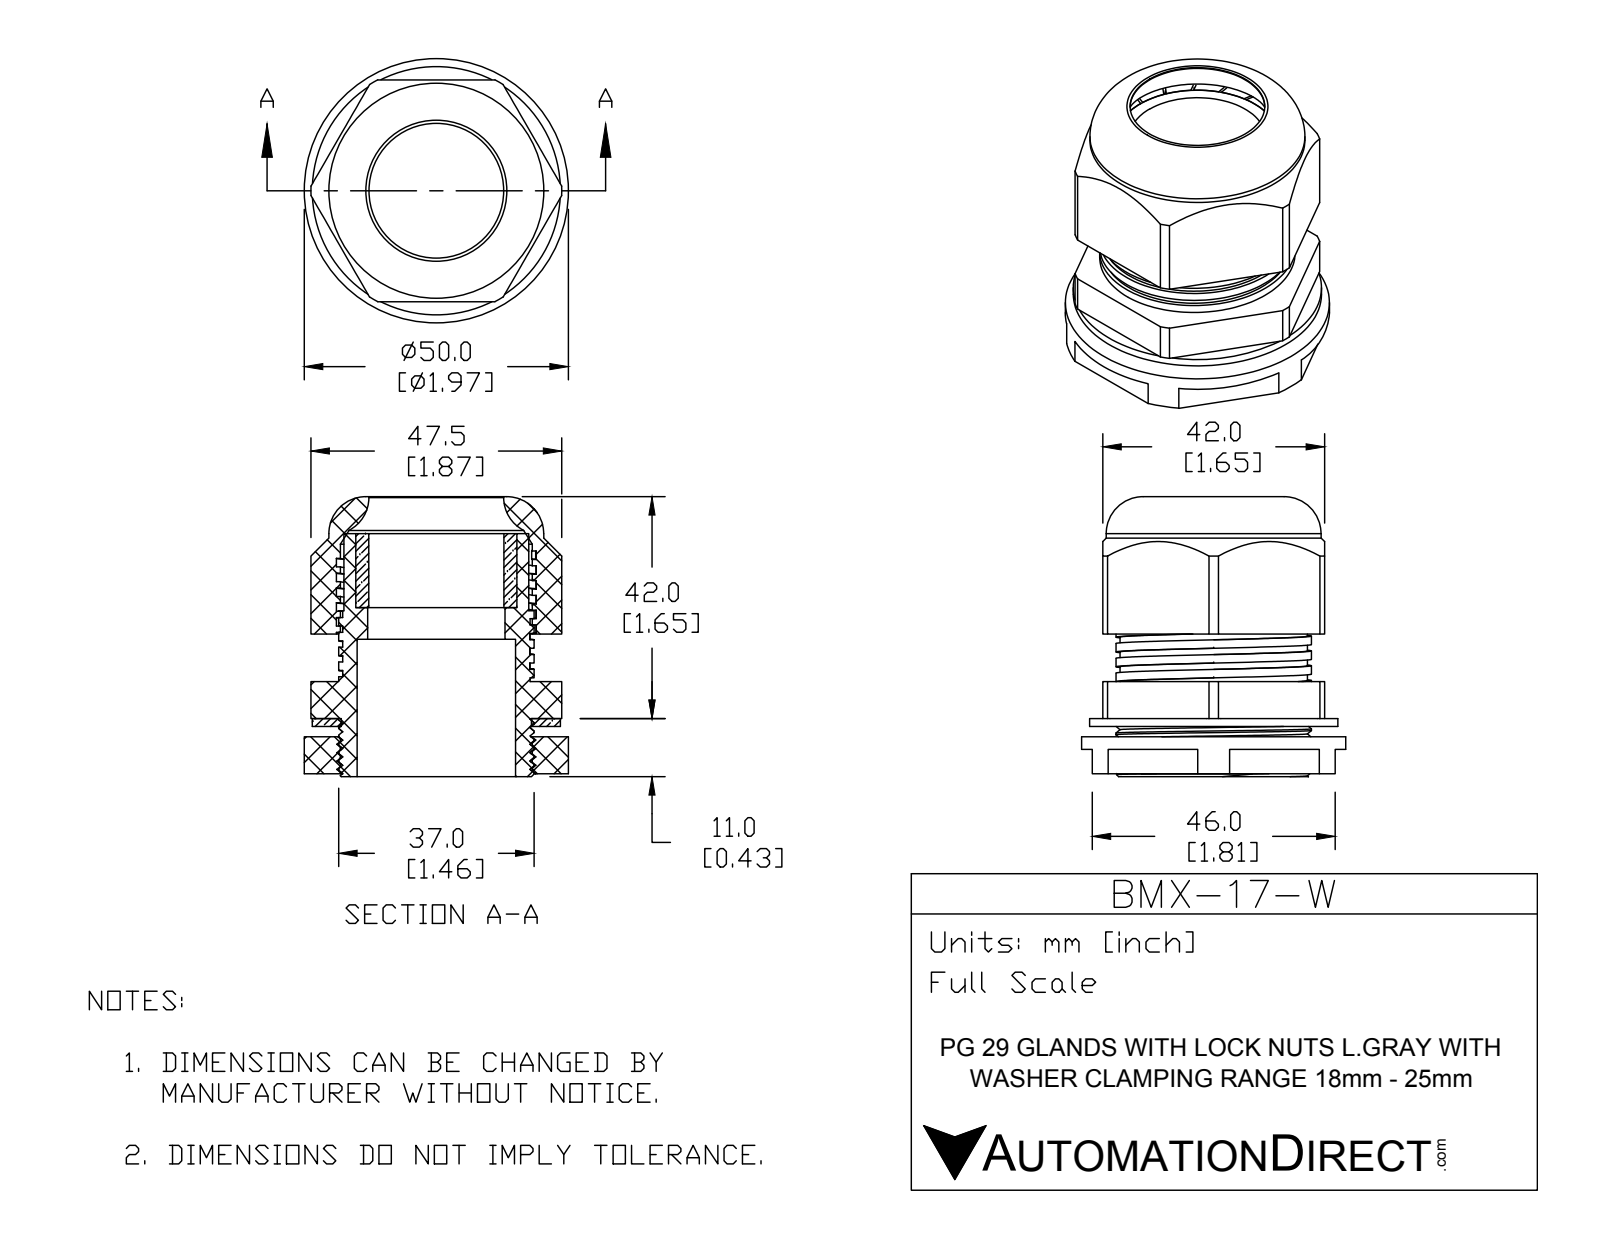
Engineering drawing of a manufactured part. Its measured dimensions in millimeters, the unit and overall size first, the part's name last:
Units: millimetres
Overall size (bounding box): 53 × 50 × 50
Round holes (diameter × count): ⌀25.5 ×1, ⌀25.58 ×1, ⌀26 ×1, ⌀30 ×1, ⌀30.5 ×1, ⌀36 ×1, ⌀36.33 ×1
Round bosses / shafts (diameter × count): ⌀50 ×1, ⌀47 ×1, ⌀40.7 ×1, ⌀37 ×1, ⌀35 ×1
Partial cylindrical surfaces — rounded edges, fillets, slot ends (radius × count): R23.75 ×1
Main face-to-face distances: 42, 7, 10.45, 3.45, 14, 8.95, 1.95, 1.5, 46, 2
Volume: 39 425 mm³ · Surface area: 31 013 mm²
Bodies: 5 solids, 220 faces (113 planar, 86 cylindrical, 21 other)
Part name (STEP PRODUCT): BMX-17-W
STEP written by: SolidWorks 2015 (CONFIG_CONTROL_DESIGN)
